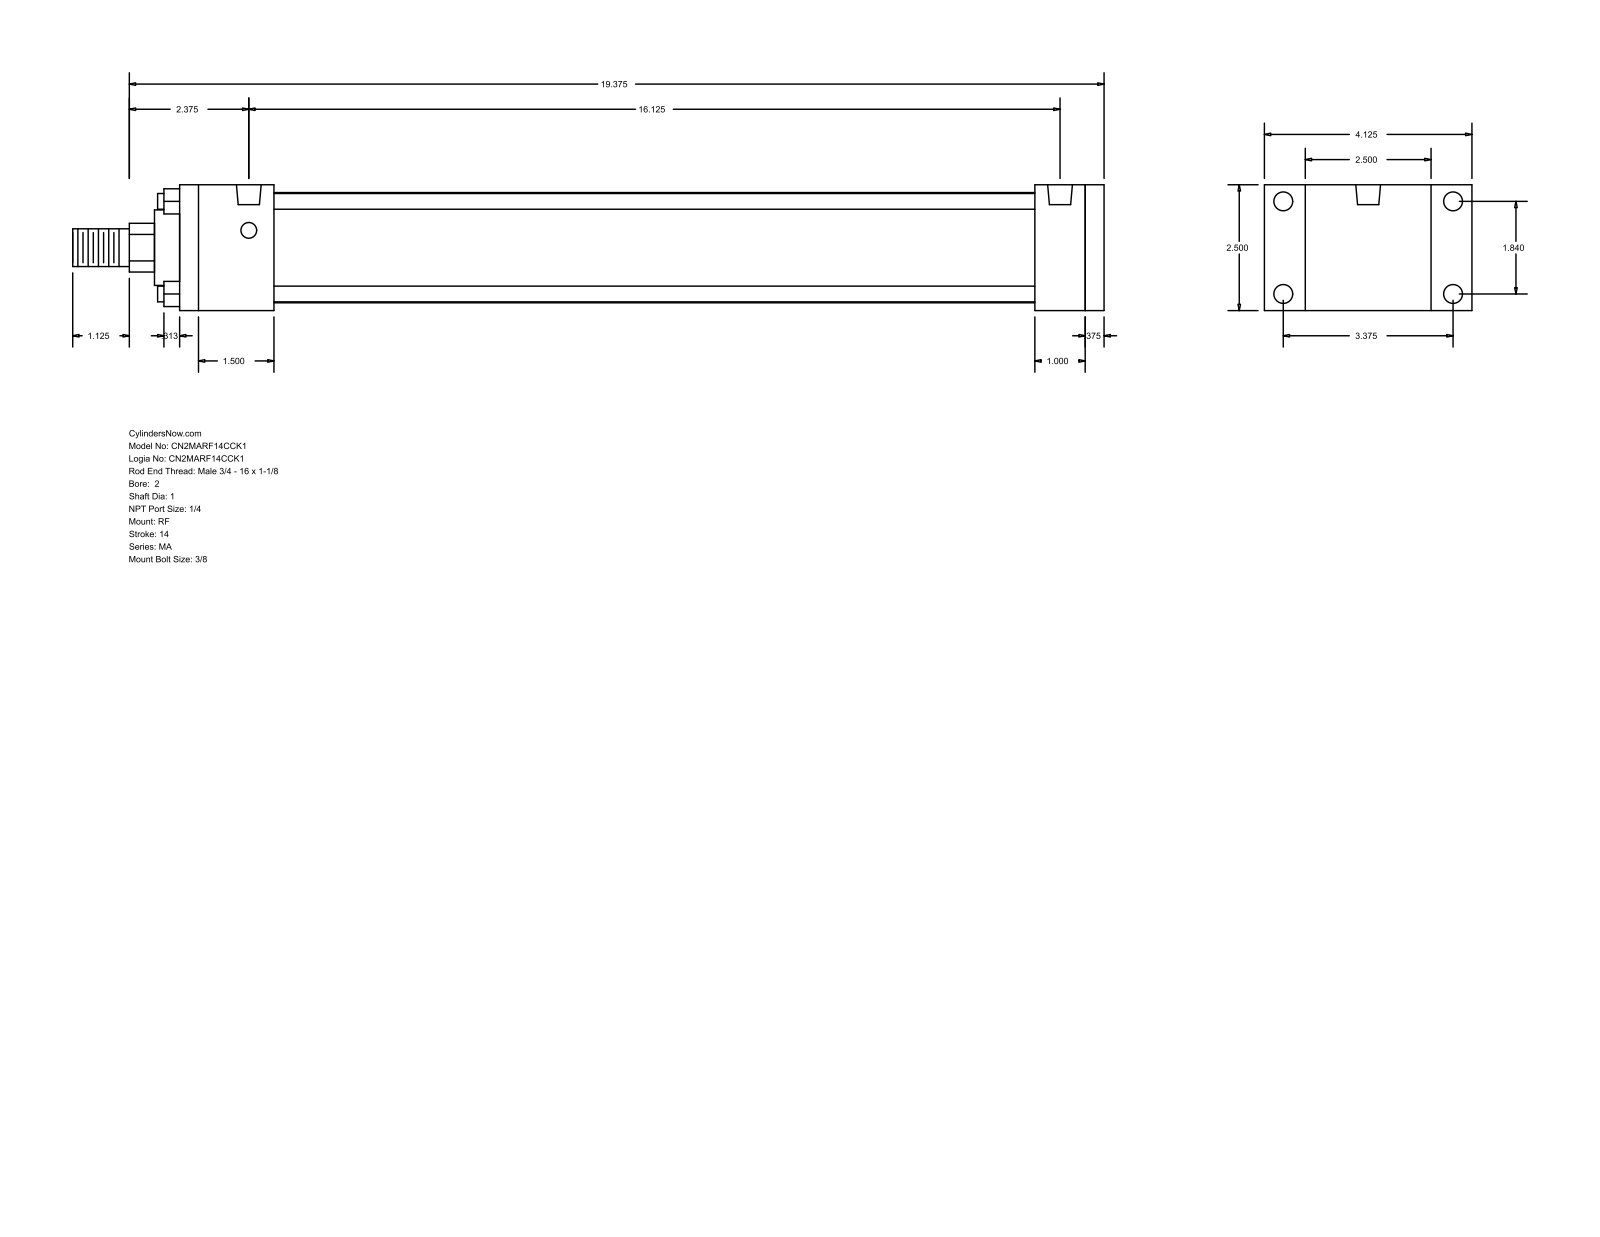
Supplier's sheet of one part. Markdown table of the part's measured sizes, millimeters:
| quantity | value |
| --- | --- |
| part name | MA_RF__0200_1 |
| STEP written by | GSSL Pune (CONFIG_CONTROL_DESIGN) |
| units | millimeters |
| bodies | 0 solids, 92 faces (64 planar, 28 cylindrical, 0 other) |
| overall size | 520.7 × 104.78 × 63.5 |
| round holes (diameter × count) | 7.94 × 4, 9.53 × 4, 12.49 × 2 |
| round bosses / shafts (diameter × count) | 7.94 × 4, 55.63 × 1, 38.1 × 1, 25.4 × 1, 19.05 × 1 |
| partial cylindrical surfaces (radius × count) | 12.29 × 1 |
| main face-to-face distances | 63.5, 457.2, 9.52, 466.72, 25.4, 20.64, 12.7, 47.63, 409.57, 419.09 |
| hole center spacings | 46.74, 85.72, 97.63, 409.57 |
